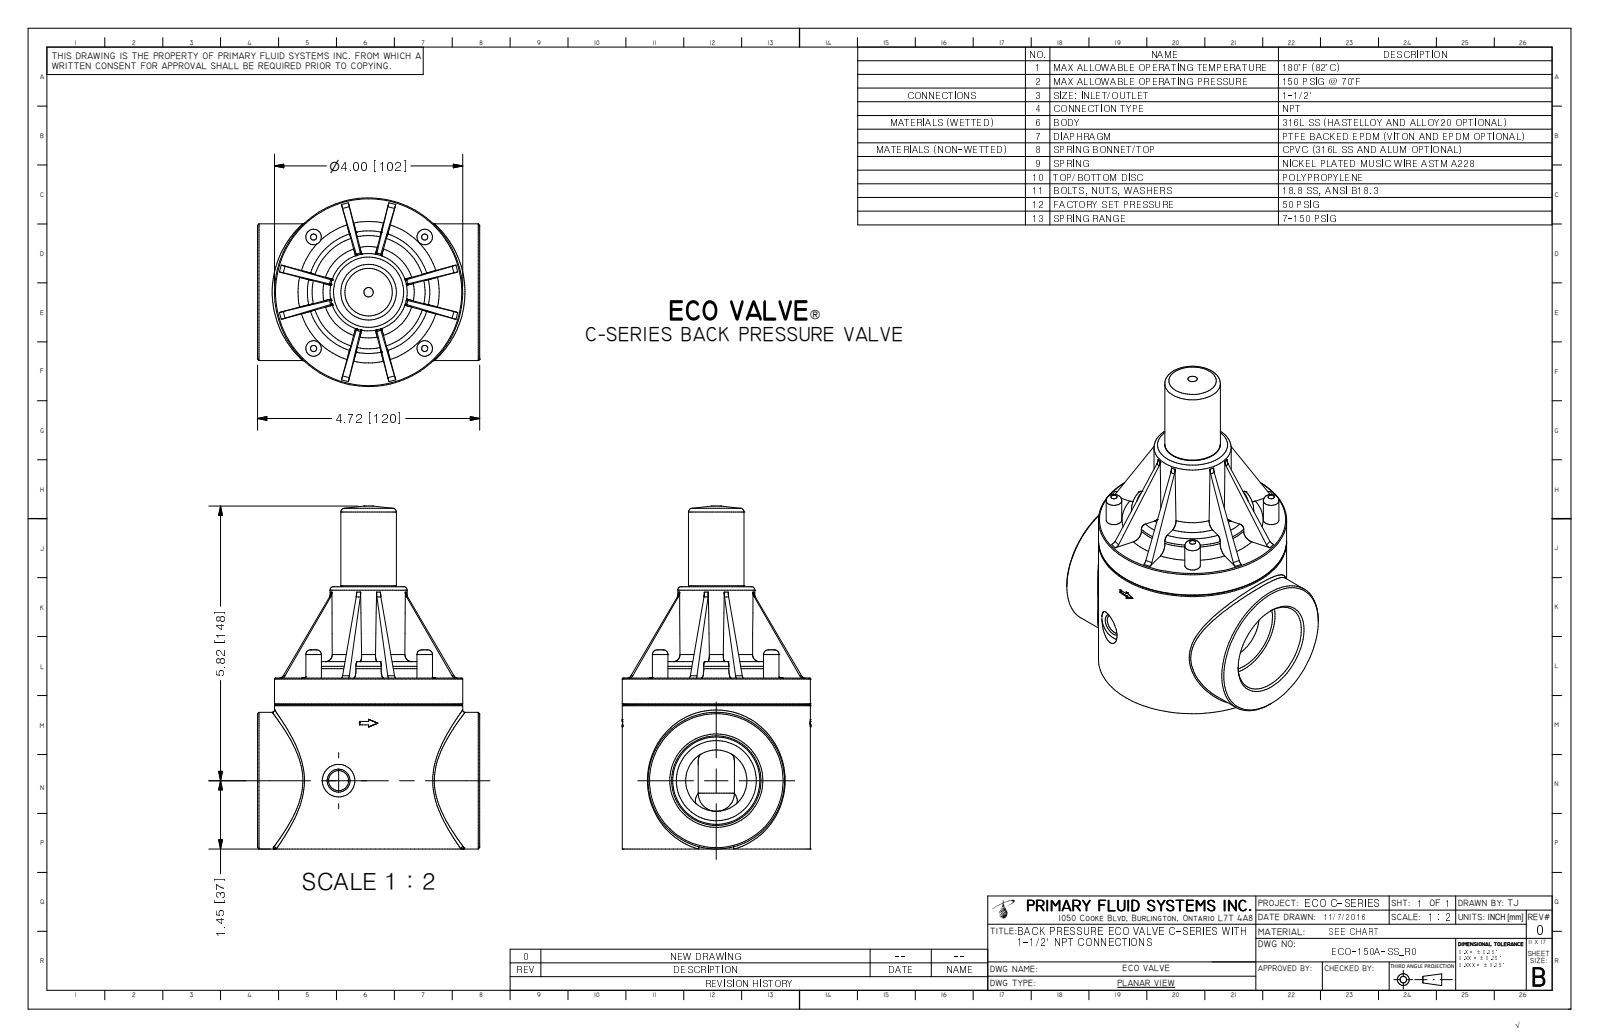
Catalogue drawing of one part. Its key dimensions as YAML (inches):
part_name: "ECO-150A-SS_R0"
step_written_by: "Autodesk Inventor 2009 (AUTOMOTIVE_DESIGN)"
units: inches
bodies: {solids: 1, faces: 228, planar: 102, cylindrical: 53, other: 73}
overall_size: [7.274, 4.72, 4]
volume: 55.37
surface_area: 136.8
round_holes:
  - {diameter: 0.23, count: 4}
  - {diameter: 0.257, count: 1}
  - {diameter: 0.426, count: 1}
  - {diameter: 0.691, count: 1}
round_bosses_or_shafts:
  - {diameter: 0.33, count: 4}
  - {diameter: 4, count: 1}
  - {diameter: 2.9, count: 1}
  - {diameter: 2.6, count: 1}
  - {diameter: 1.64, count: 1}
  - {diameter: 1.18, count: 1}
  - {diameter: 0.256, count: 1}
partial_cylinders:
  - {radius: 0.1, count: 8}
  - {radius: 0.128, count: 7}
  - {radius: 0.2, count: 6}
  - {radius: 0.129, count: 3}
  - {radius: 1.98, count: 1}
face_to_face_distances: [0.807, 3.913, 3.624, 4.72, 3.106, 0.35, 3.974, 5.564, 1.94, 1.59]
hole_center_spacings: [2.363, 2.363, 3.342, 3.341]
